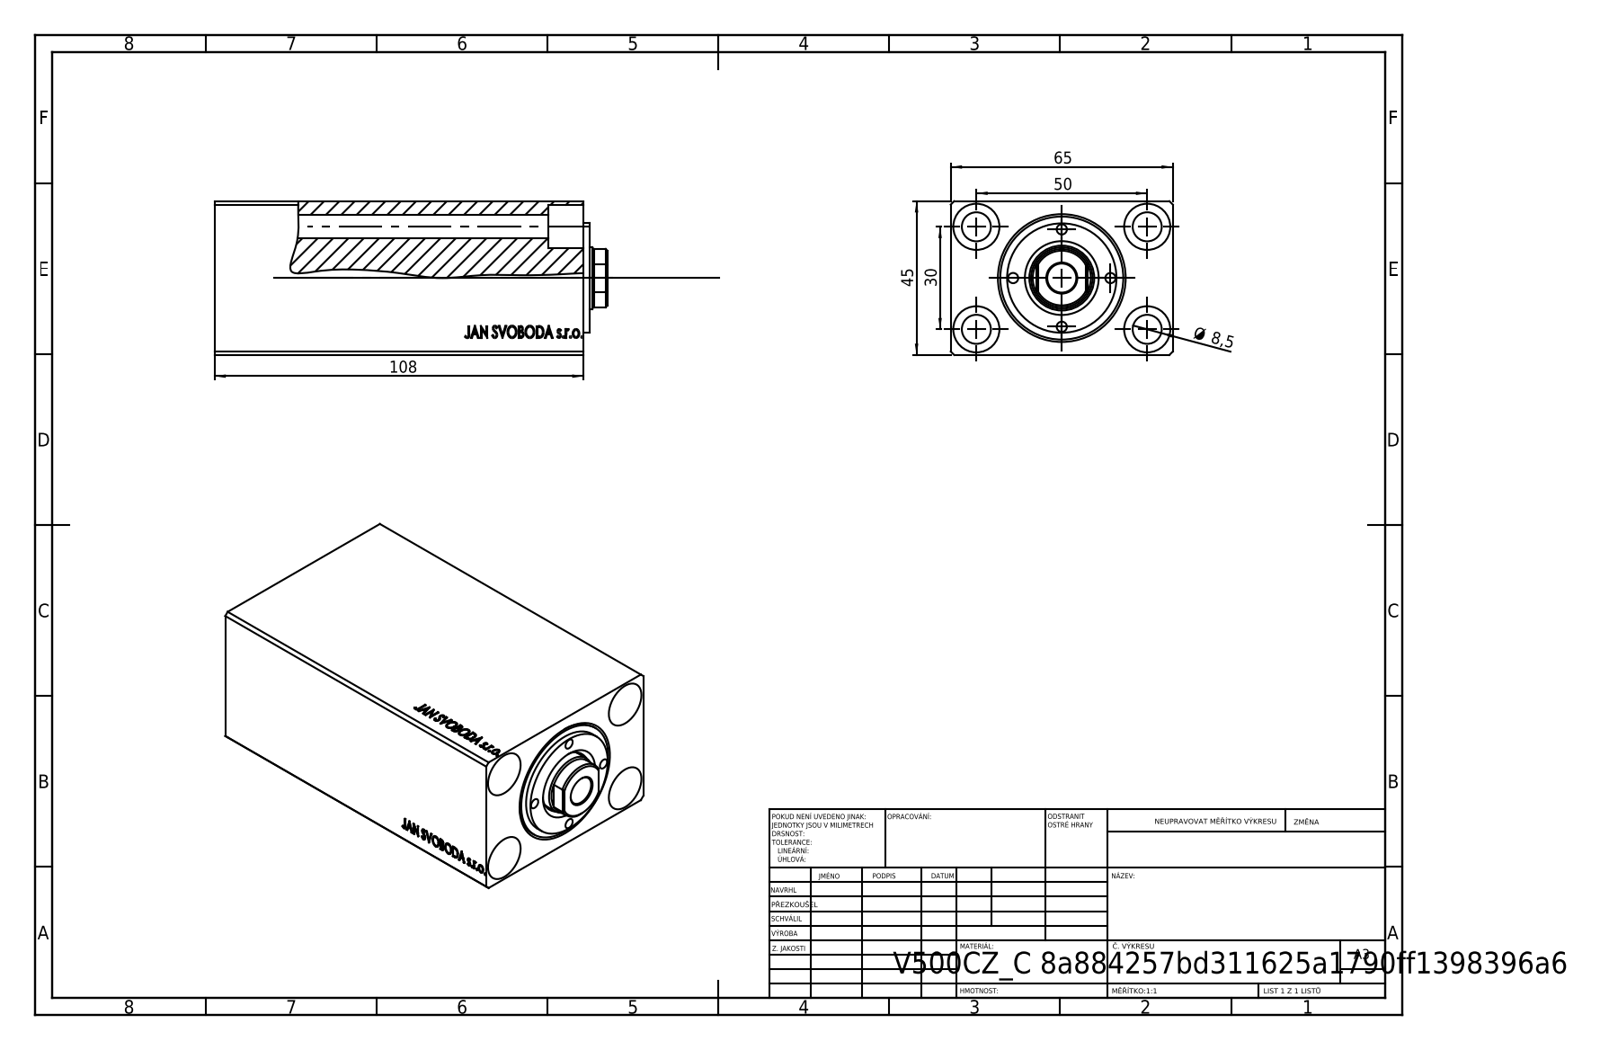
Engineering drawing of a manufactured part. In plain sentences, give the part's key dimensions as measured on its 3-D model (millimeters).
Its 3-D file was written by "SolidWorks 2019 (CONFIG_CONTROL_DESIGN)". It is 1 solid with 818 faces: 394 planar, 42 cylindrical and 382 other. Overall it measures 108 by 65 by 45 millimeters. Its volume is 201 754 cubic millimeters and its surface area 52 639 square millimeters. Round holes: 4 of diameter 8.5, 4 of diameter 13.5, 2 of diameter 5.5, 2 of diameter 13.6, 2 of diameter 20, 1 of diameter 25, 1 of diameter 36. The main face-to-face distances are 45, 65, 108, 107.8, 10.33, 97.67, 58, 49.8, 50, 96.5. The hole center spacings are 29.15, 30, 50, 58.31, 75.
